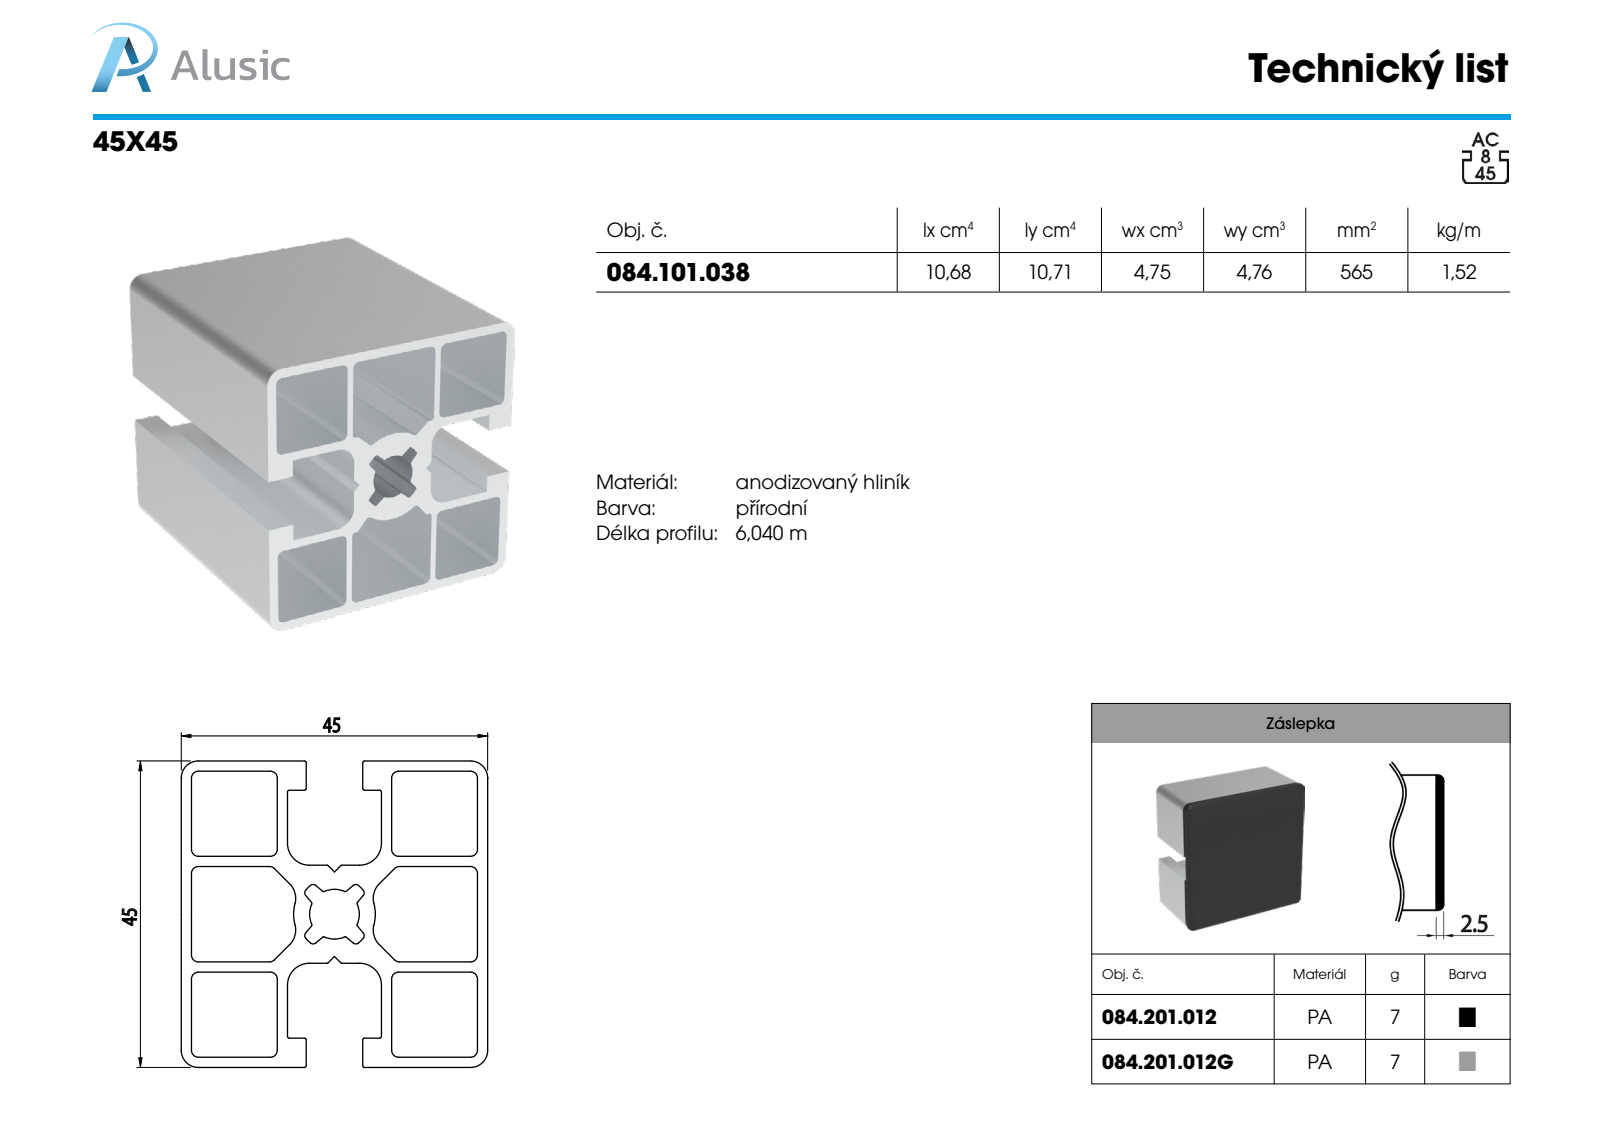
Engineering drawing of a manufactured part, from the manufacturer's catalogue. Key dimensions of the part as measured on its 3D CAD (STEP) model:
Part name (STEP PRODUCT): 084.101.038
STEP written by: SolidWorks 2018 (AUTOMOTIVE_DESIGN)
Units: millimetres
Bodies: 1 solid, 137 faces (66 planar, 71 cylindrical, 0 other)
Overall size (bounding box): 100 × 45 × 45
Volume: 54 999 mm³ · Surface area: 61 005 mm²
Partial cylindrical surfaces — rounded edges, fillets, slot ends (radius × count): R1 ×20, R0.2 ×16, R0.5 ×12, R2.5 ×4, R3 ×4, R3.65 ×1, R5.5 ×1, R7.5 ×1
Main face-to-face distances: 1.5, 43.5, 45, 15, 42, 30, 14, 31, 12.5, 13.5
